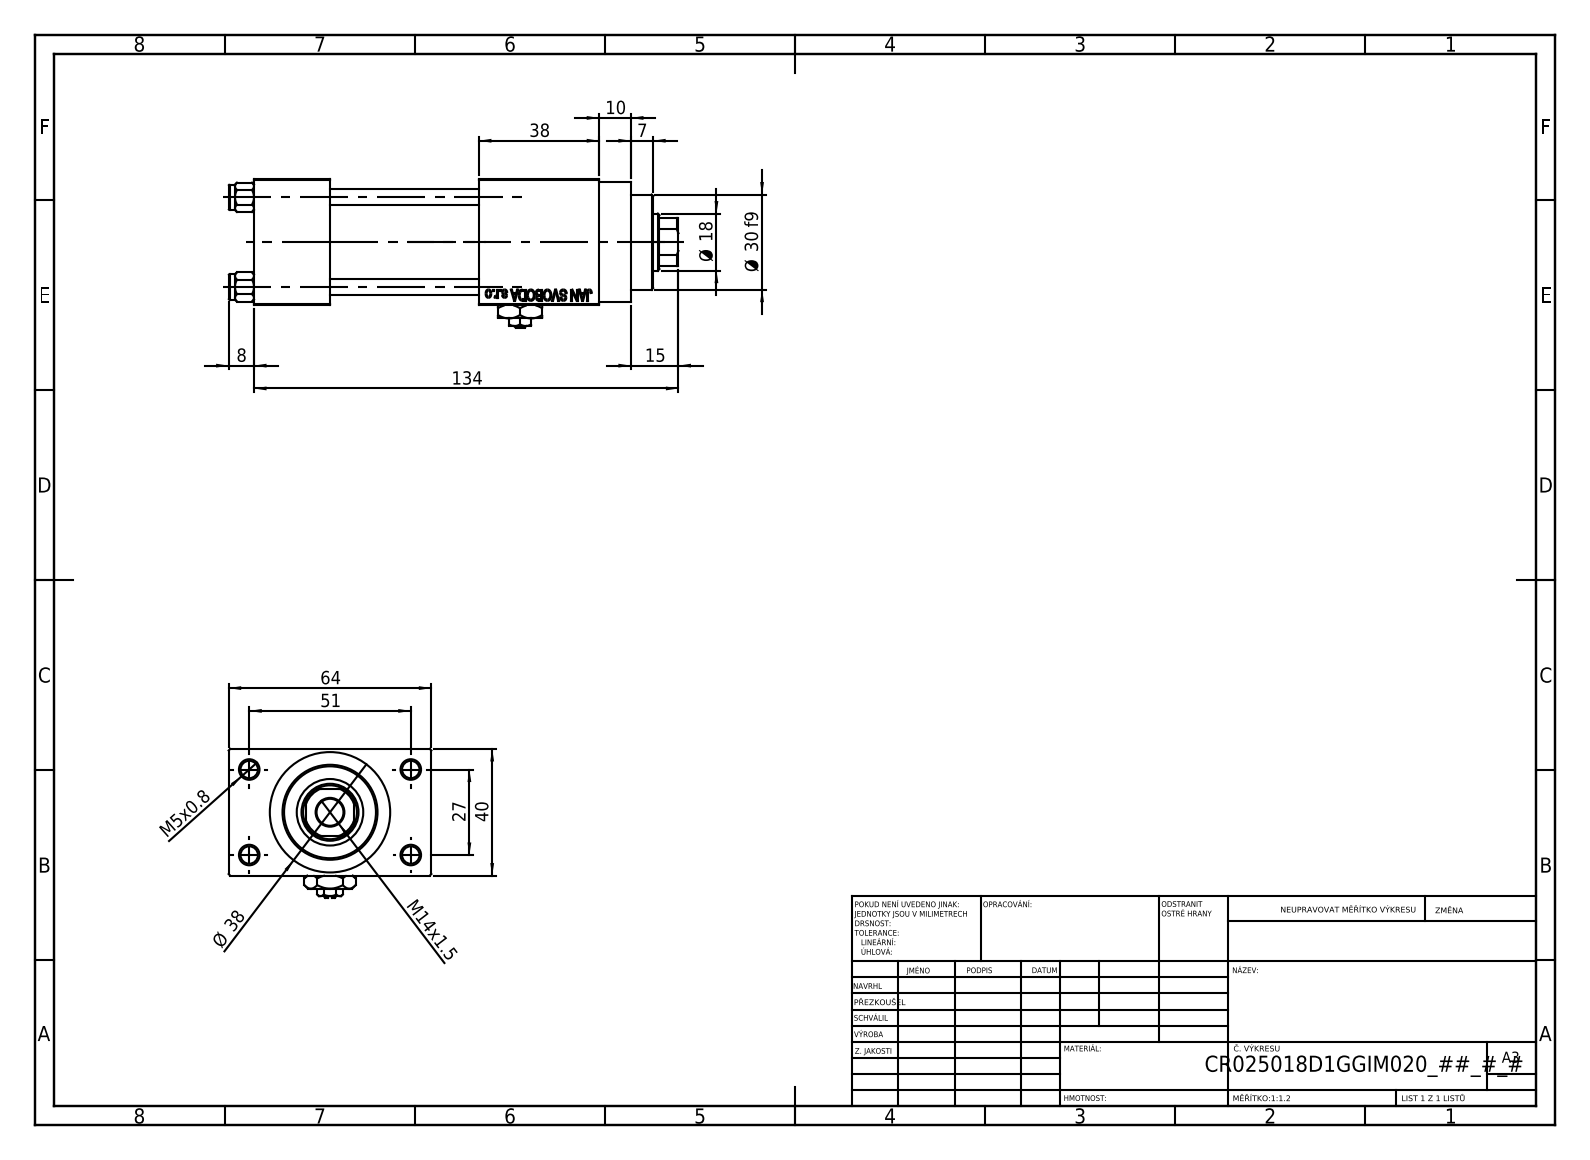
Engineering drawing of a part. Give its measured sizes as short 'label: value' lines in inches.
name: V215CR_VCP_D; V215CR_D_TYCINKA; V215CR_D_Body; NUT_M5_D (+2 more)
written by: SolidWorks 2019 (CONFIG_CONTROL_DESIGN)
unit: in
bodies: 12 solids, 1147 faces (518 planar, 91 cylindrical, 538 other)
size: 5.591 × 2.52 × 1.85
volume: 11.04 in³; area: 100.4 in²
holes: 4× ⌀0.197, 4× ⌀0.217, 3× ⌀0.787, 2× ⌀0.276, 2× ⌀0.518, 1× ⌀0.335, 1× ⌀0.709, 1× ⌀0.827, 1× ⌀0.984, 1× ⌀1.181
bosses: 4× ⌀0.315, 1× ⌀1.496, 1× ⌀1.22
rounds: 1× R0.335
face distances: 1.575, 0.472, 2.047, 1.85, 0.945, 2.795, 2.52, 1.496, 3.346, 4.291
hole spacings: 0.448, 0.788, 1.114, 1.136, 1.177, 1.561, 1.903, 1.063
